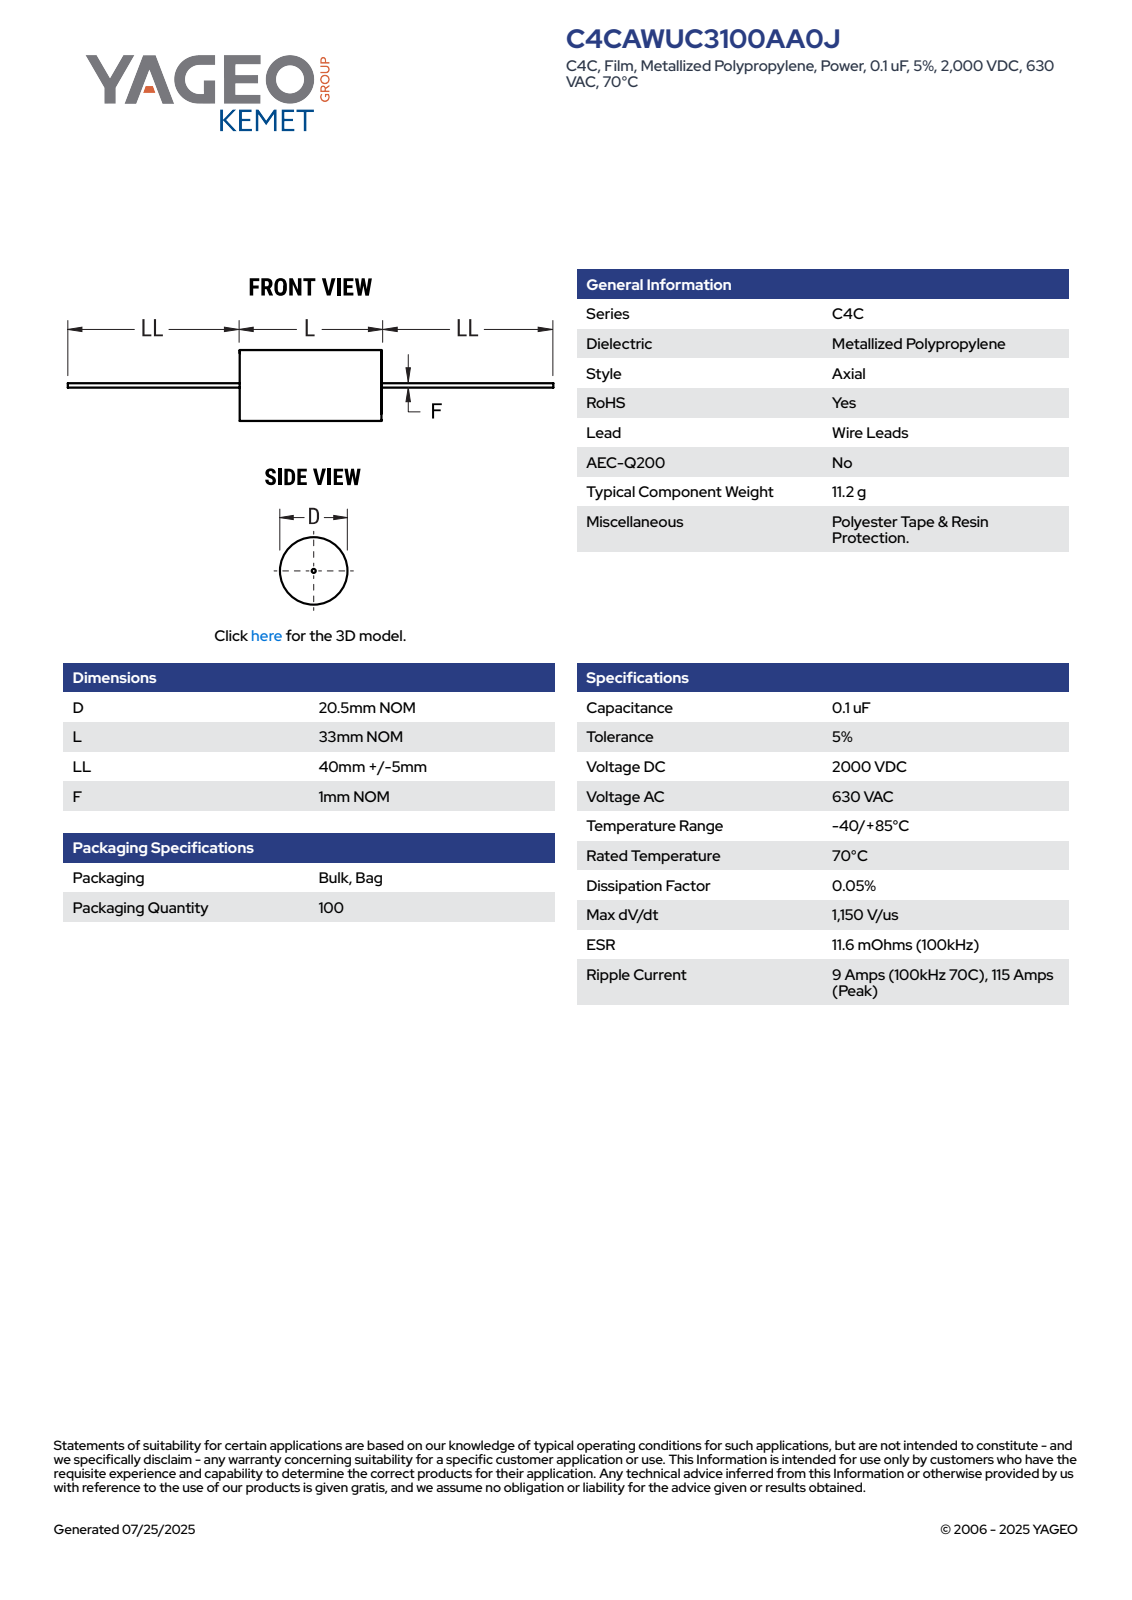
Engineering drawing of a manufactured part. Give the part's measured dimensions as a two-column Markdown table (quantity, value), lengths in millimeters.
| quantity | value |
| --- | --- |
| part name | CFP_ACWF_20.5X33_D20.5L33LL45F1 |
| STEP written by | SolidWorks 2014 (AUTOMOTIVE_DESIGN) |
| units | millimeters |
| bodies | 2 solids, 87 faces (28 planar, 28 cylindrical, 31 other) |
| overall size | 123 × 20.5 × 20.5 |
| volume | 10 963 mm³ |
| surface area | 3 728 mm² |
| round bosses / shafts (diameter × count) | 20.5 × 1, 1 × 1 |
| partial cylindrical surfaces (radius × count) | 10.24 × 1 |
| main face-to-face distances | 33.01, 33, 45, 78, 44.99, 123, 78.01 |
